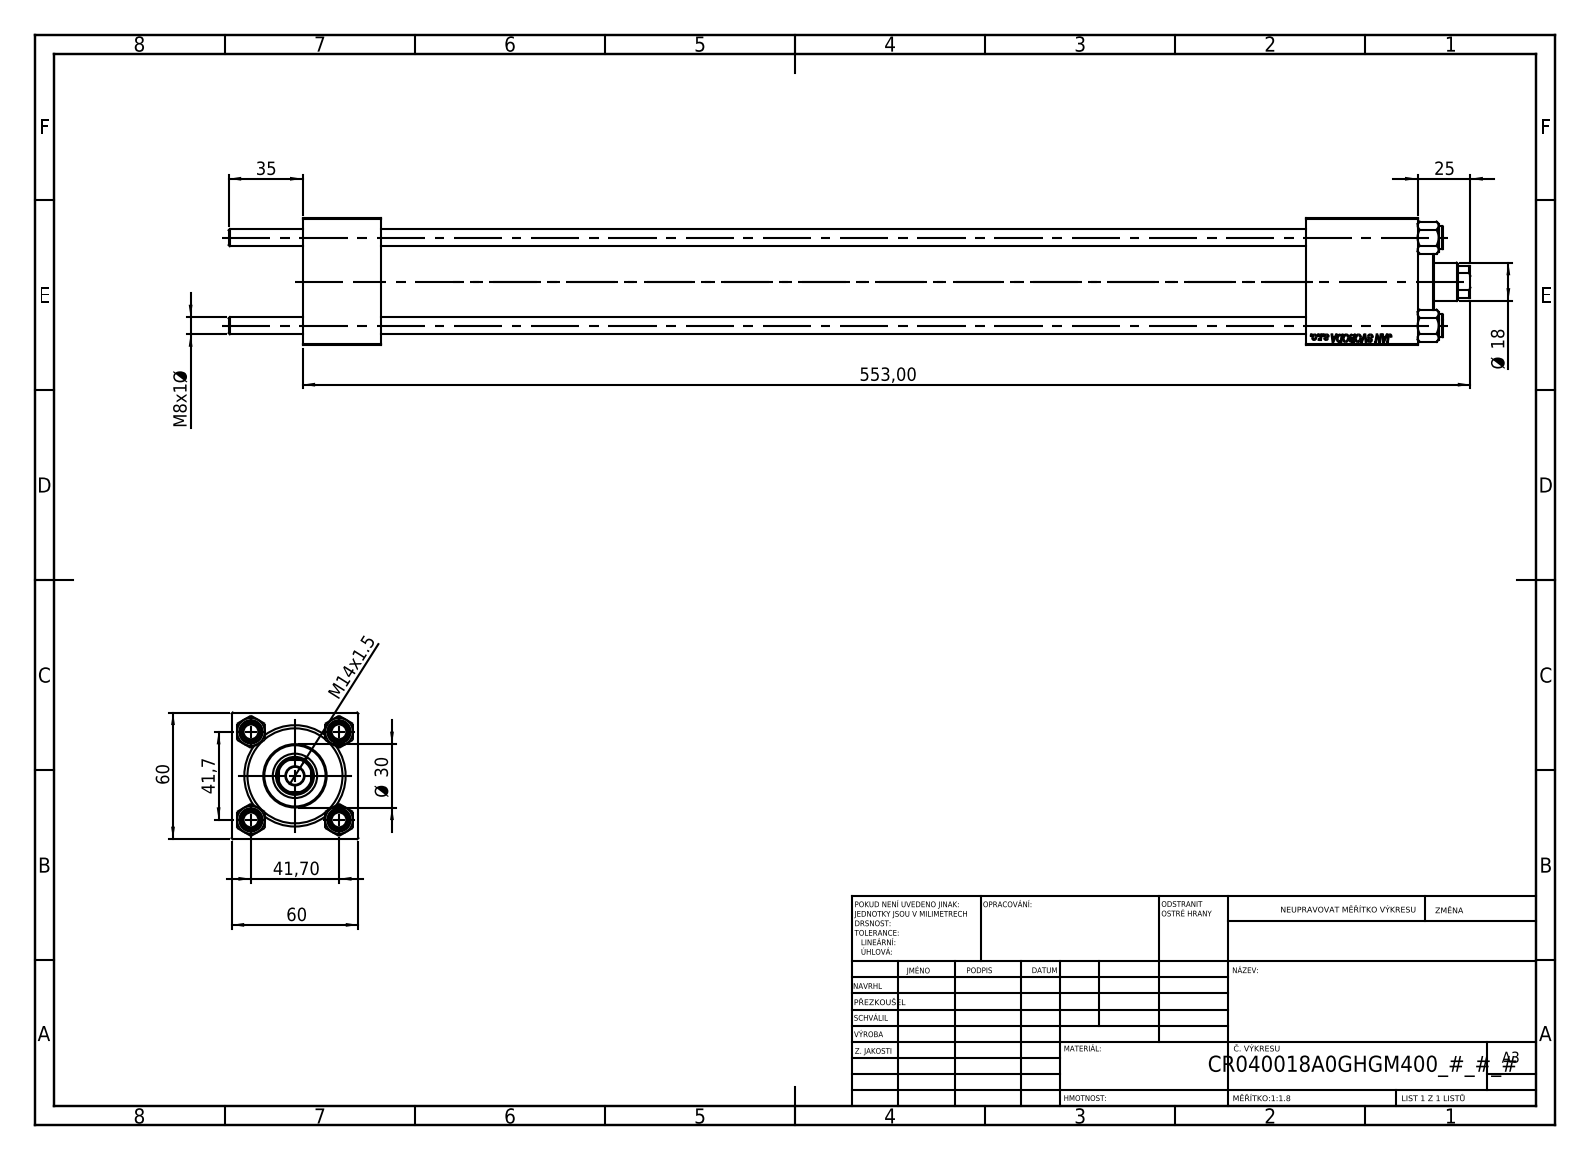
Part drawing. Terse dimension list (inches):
name: V215CR_BODY_A; V215CR_VCP; NUT_M5; V215_VC_A (+1 more)
written by: SolidWorks 2019 (CONFIG_CONTROL_DESIGN)
unit: in
bodies: 11 solids, 1135 faces (521 planar, 78 cylindrical, 536 other)
size: 23.15 × 2.362 × 2.362
volume: 45.22 in³; area: 428.4 in²
holes: 4× ⌀0.315, 2× ⌀0.276, 2× ⌀0.656, 2× ⌀0.945, 1× ⌀0.335, 1× ⌀0.709, 1× ⌀0.827, 1× ⌀1.22, 1× ⌀1.575, 1× ⌀1.772
bosses: 4× ⌀0.433, 1× ⌀1.811, 1× ⌀1.181
rounds: 1× R0.335
face distances: 2.362, 1.457, 20.787, 19.331, 2.087, 18.701, 17.244, 19.657, 18.201, 0.957
hole spacings: 1.161, 1.642, 2.322, 18.602
